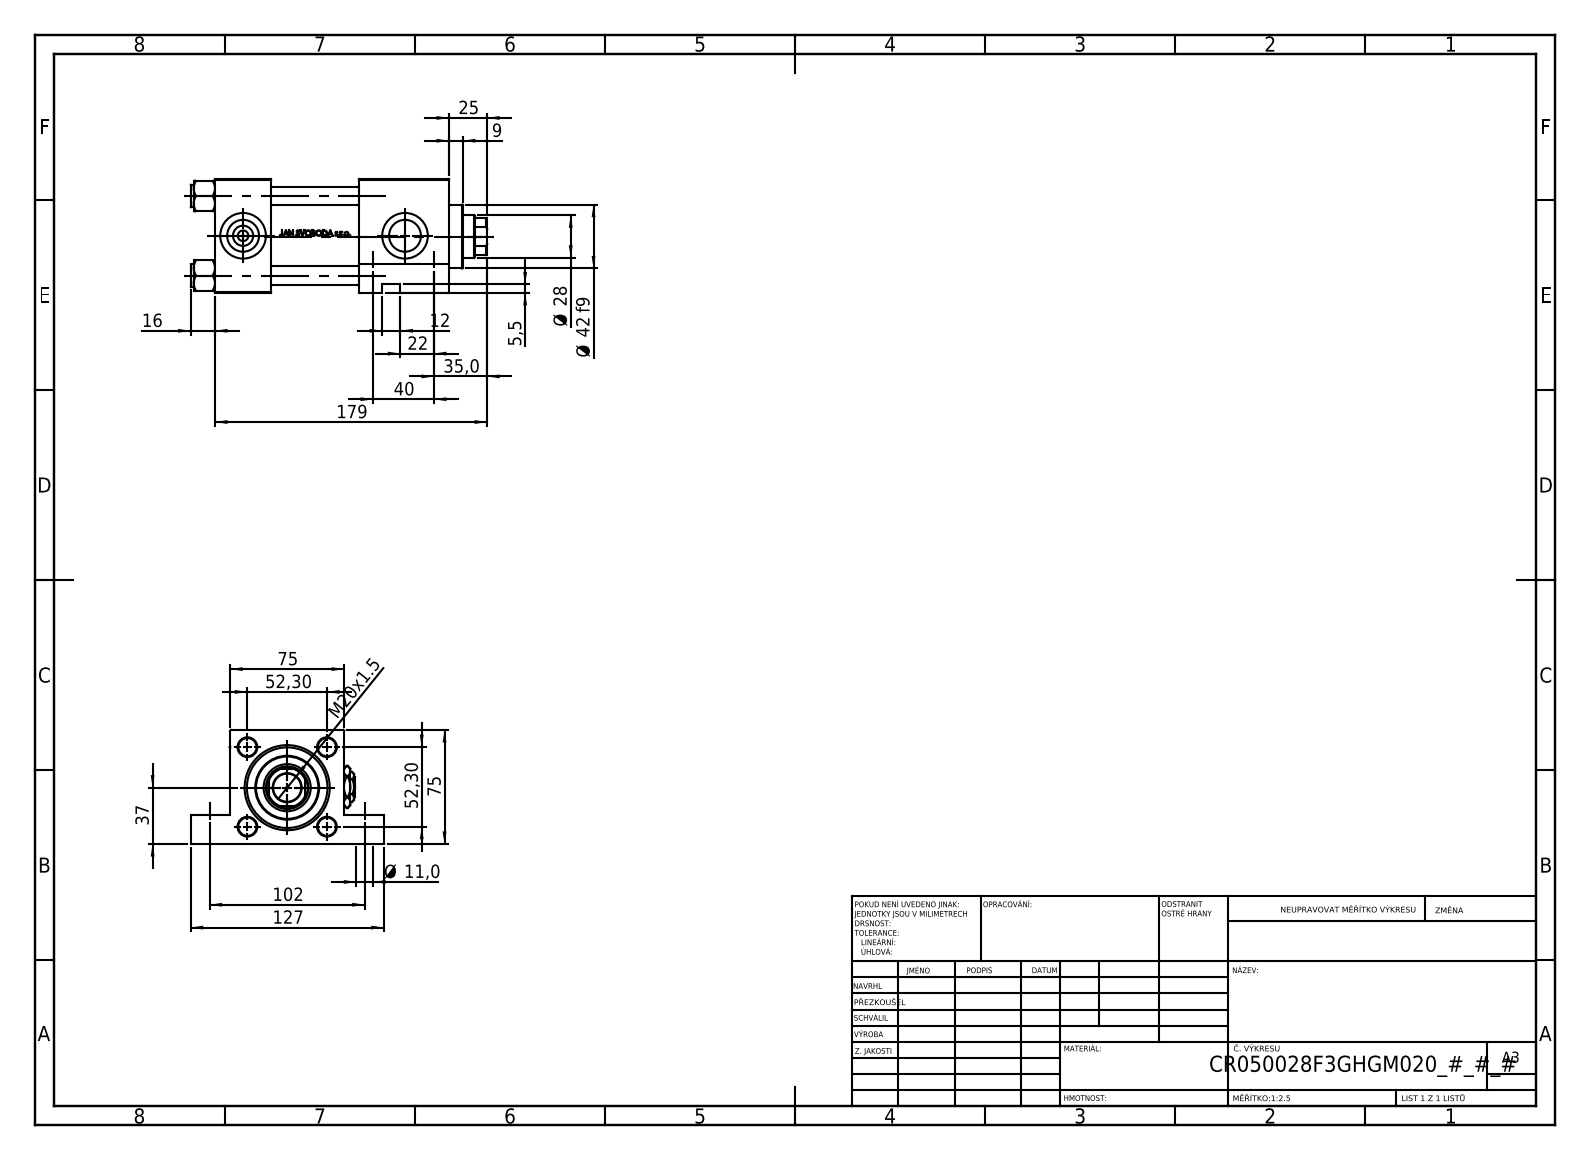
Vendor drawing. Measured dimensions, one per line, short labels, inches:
name: V215CR_VCP_F; Zatka_pro_OIL_PORT; V215CR_F_Body; V215_VC_A (+2 more)
written by: SolidWorks 2019 (CONFIG_CONTROL_DESIGN)
unit: in
bodies: 13 solids, 1199 faces (483 planar, 134 cylindrical, 582 other)
size: 7.677 × 5 × 2.953
volume: 43.59 in³; area: 254.6 in²
holes: 4× ⌀0.472, 3× ⌀0.825, 3× ⌀1.181, 2× ⌀0.276, 2× ⌀0.433, 2× ⌀0.433, 1× ⌀0.669, 1× ⌀0.728, 1× ⌀1.102, 1× ⌀1.22, 1× ⌀1.614, 1× ⌀1.969
bosses: 4× ⌀0.591, 1× ⌀2.205, 1× ⌀1.654
rounds: 1× R0.531
face distances: 2.953, 1.457, 6.063, 4.606, 3.74, 2.283, 2.323, 0.748, 2.205, 2.945
hole spacings: 2.059, 1.442, 1.47, 1.575, 2.912, 4.016, 4.313, 0.512
